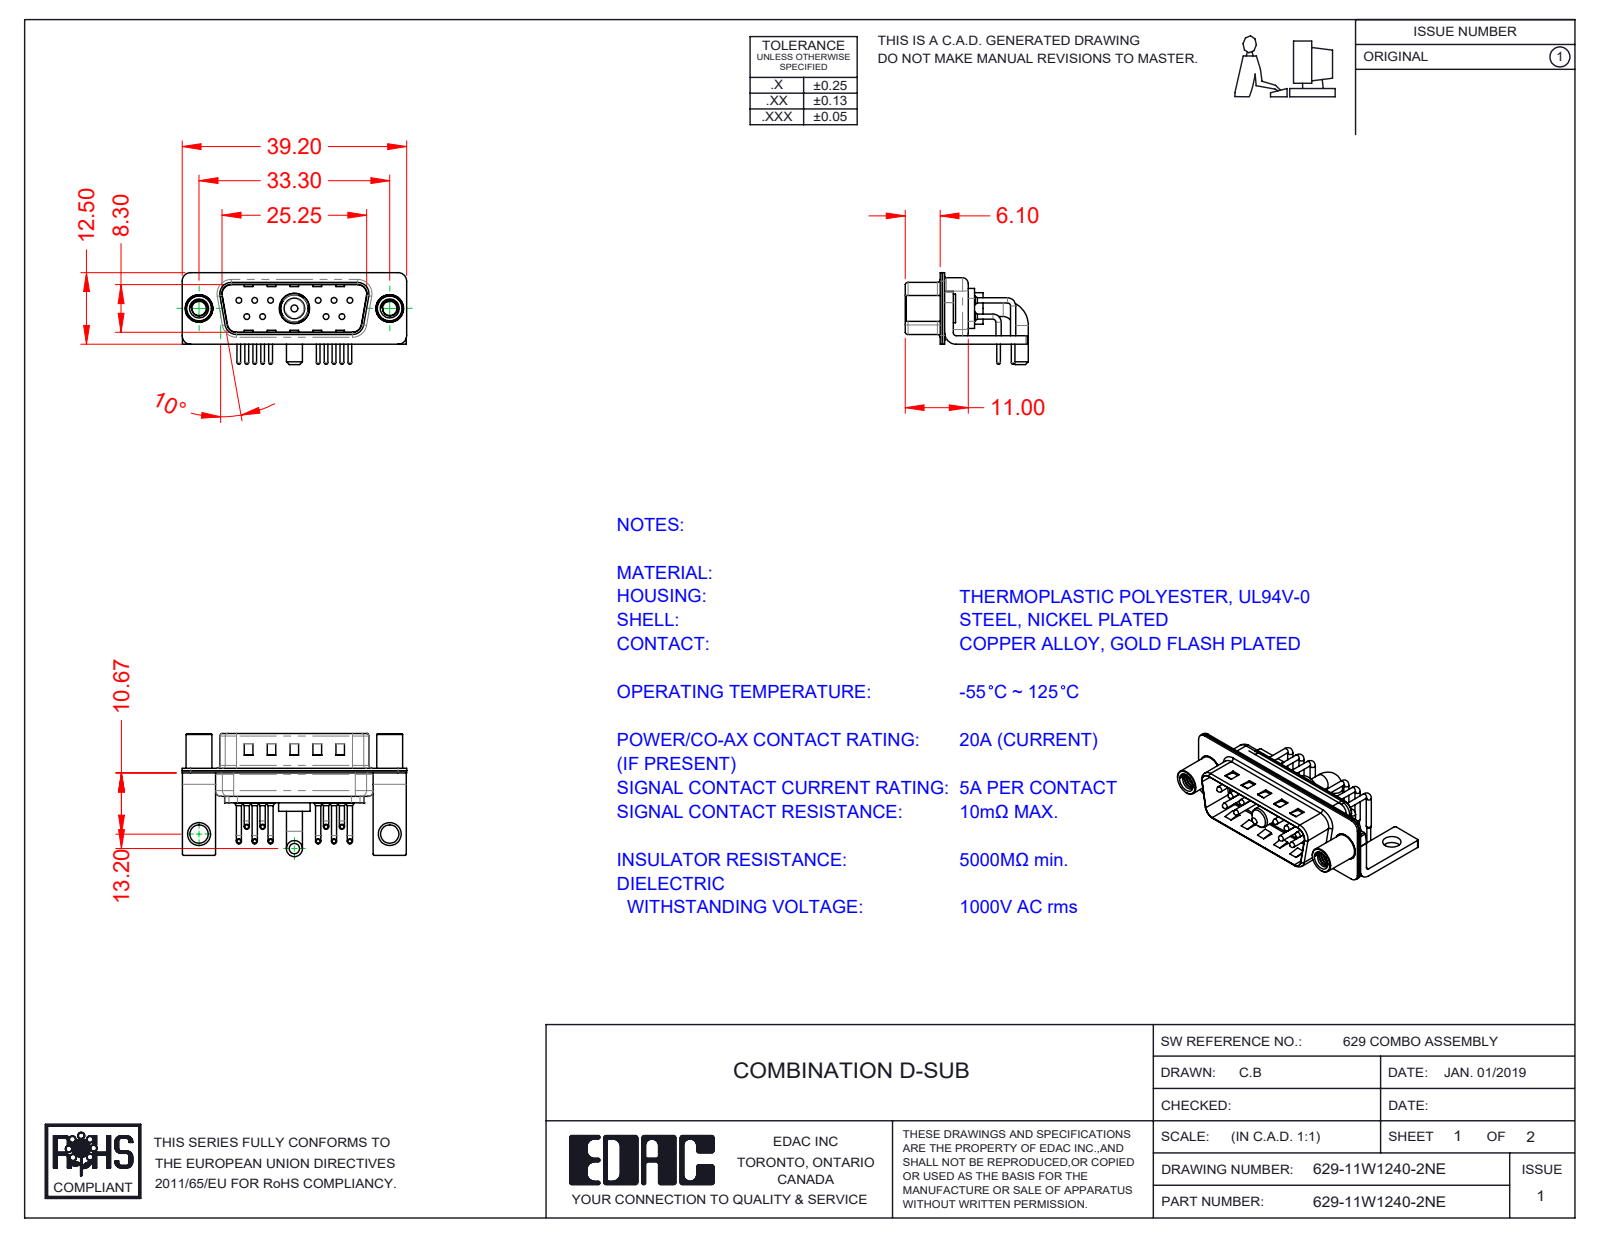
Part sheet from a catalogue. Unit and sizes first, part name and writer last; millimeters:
Units: millimetres
Overall size (bounding box): 39.2 × 21.5 × 16.05
Round holes (diameter × count): ⌀0.75 ×10, ⌀1.6 ×10, ⌀2 ×10, ⌀2.5 ×2, ⌀3.2 ×2, ⌀4 ×2, ⌀4.8 ×2, ⌀4.85 ×1, ⌀5.3 ×1
Round bosses / shafts (diameter × count): ⌀0.9 ×20, ⌀1.5 ×10, ⌀1 ×10, ⌀0.65 ×10, ⌀5 ×2, ⌀4.9 ×2, ⌀4.5 ×2, ⌀2.8 ×2
Partial cylindrical surfaces — rounded edges, fillets, slot ends (radius × count): R0.25 ×16, R1.5 ×16, R2 ×13, R1.01 ×10, R0.5 ×9, R1.6 ×8, R1 ×7, R0.6 ×4
Main face-to-face distances: 0.4, 0.8, 1.5, 9.5, 9.1, 8.7, 9.9, 0.6, 1.9, 5.2
Hole centre spacings: 3.16, 2.77, 13.85, 11.08, 16.62, 5.03, 5.04, 5.54
Volume: 2 447 mm³ · Surface area: 6 158 mm²
Bodies: 19 solids, 1594 faces (820 planar, 590 cylindrical, 184 other)
Part name (STEP PRODUCT): 629Combo Shell Front_15 Contacts; 629-11W1240-2NE; 629Combo Shell Rear_15 Contacts; 629Combo Stabilizer Bracket (+5 more)
STEP written by: SolidWorks 2020 (CONFIG_CONTROL_DESIGN)
